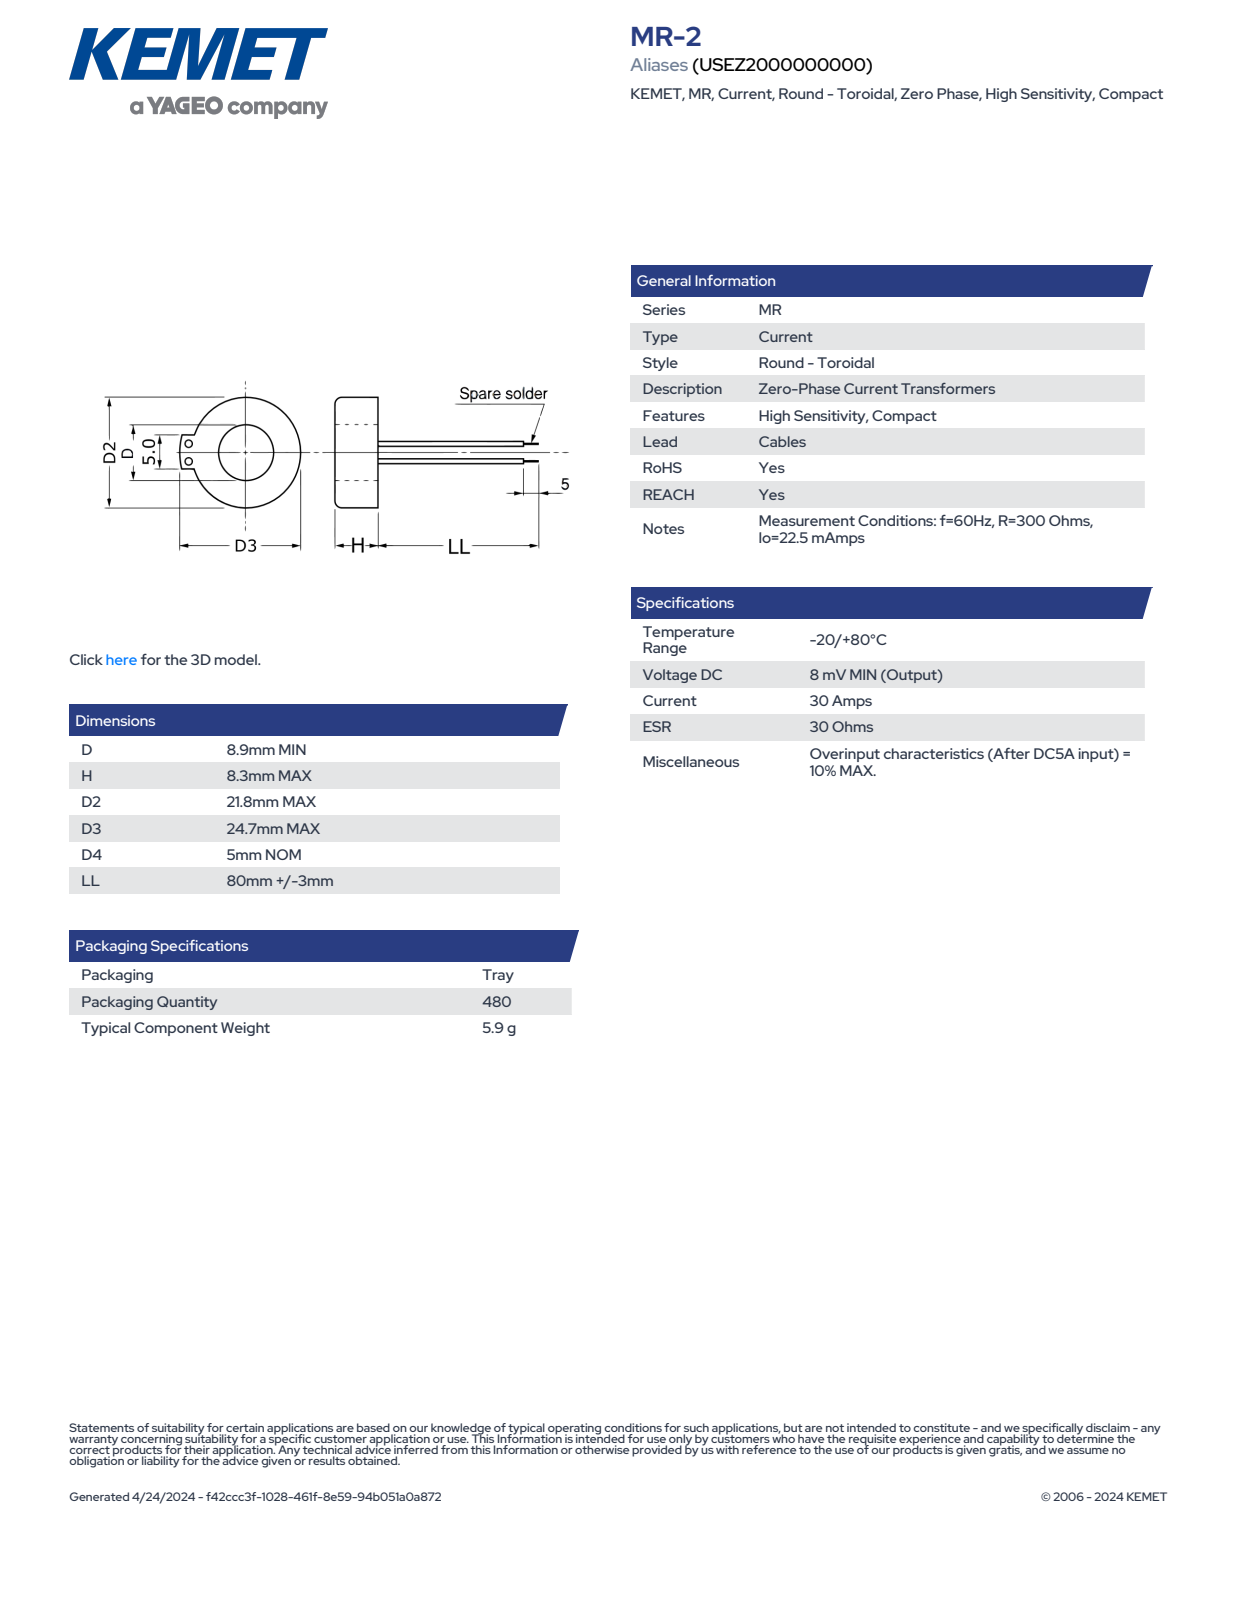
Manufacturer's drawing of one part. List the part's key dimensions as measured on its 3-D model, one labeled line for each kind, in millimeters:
Part name (STEP PRODUCT): SC_MR1_D8.9H8.3D221.8D324.7D45LL83
STEP written by: SolidWorks 2014 (AUTOMOTIVE_DESIGN)
Units: millimetres
Bodies: 1 solid, 84 faces (30 planar, 18 cylindrical, 36 other)
Overall size (bounding box): 91.3 × 24.7 × 21.8
Volume: 2 812 mm³ · Surface area: 1 979 mm²
Round holes (diameter × count): ⌀8.9 ×1
Round bosses / shafts (diameter × count): ⌀1 ×2, ⌀0.65 ×2, ⌀21.8 ×1
Partial cylindrical surfaces — rounded edges, fillets, slot ends (radius × count): R1 ×2, R10.89 ×1
Main face-to-face distances: 8.3, 5, 78, 86.3, 83, 91.3, 3.14, 5.16, 88.16, 83.16
